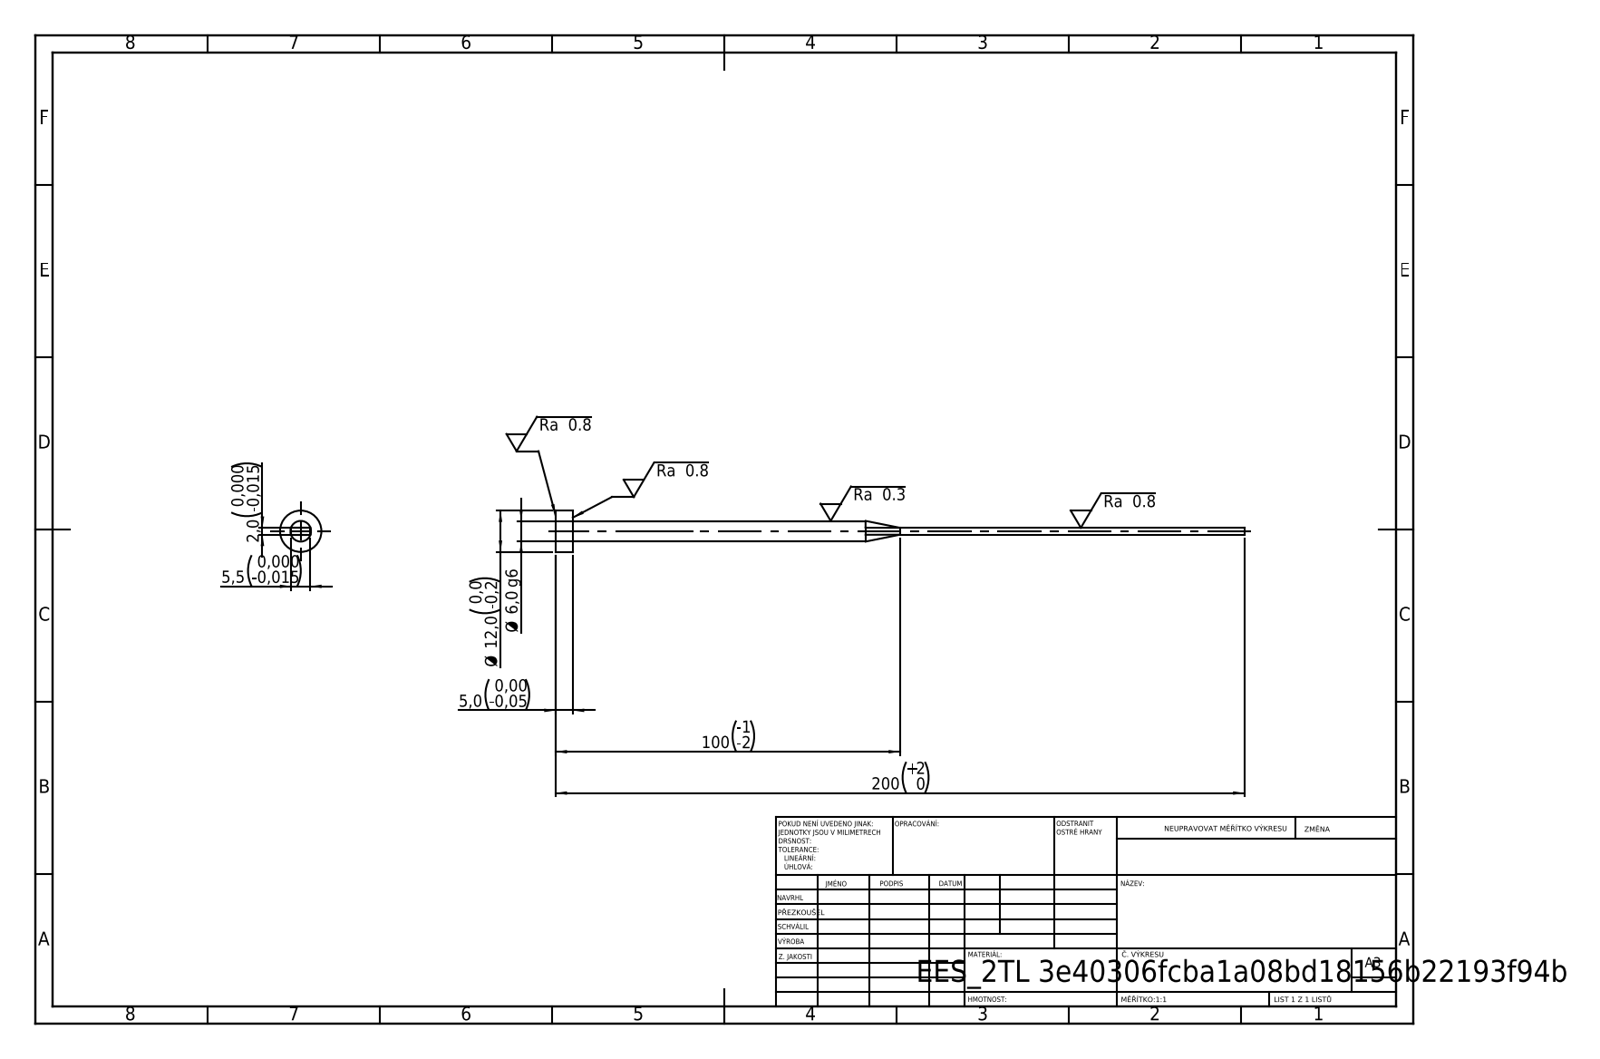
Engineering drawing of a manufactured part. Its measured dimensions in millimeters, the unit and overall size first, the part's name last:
Units: millimetres
Overall size (bounding box): 200 × 12 × 12
Round bosses / shafts (diameter × count): ⌀12 ×1, ⌀6 ×1
Main face-to-face distances: 2, 5.5, 5, 200, 195
Volume: 4 260 mm³ · Surface area: 3 665 mm²
Bodies: 1 solid, 15 faces (7 planar, 4 cylindrical, 4 other)
STEP written by: SolidWorks 2019 (CONFIG_CONTROL_DESIGN)
